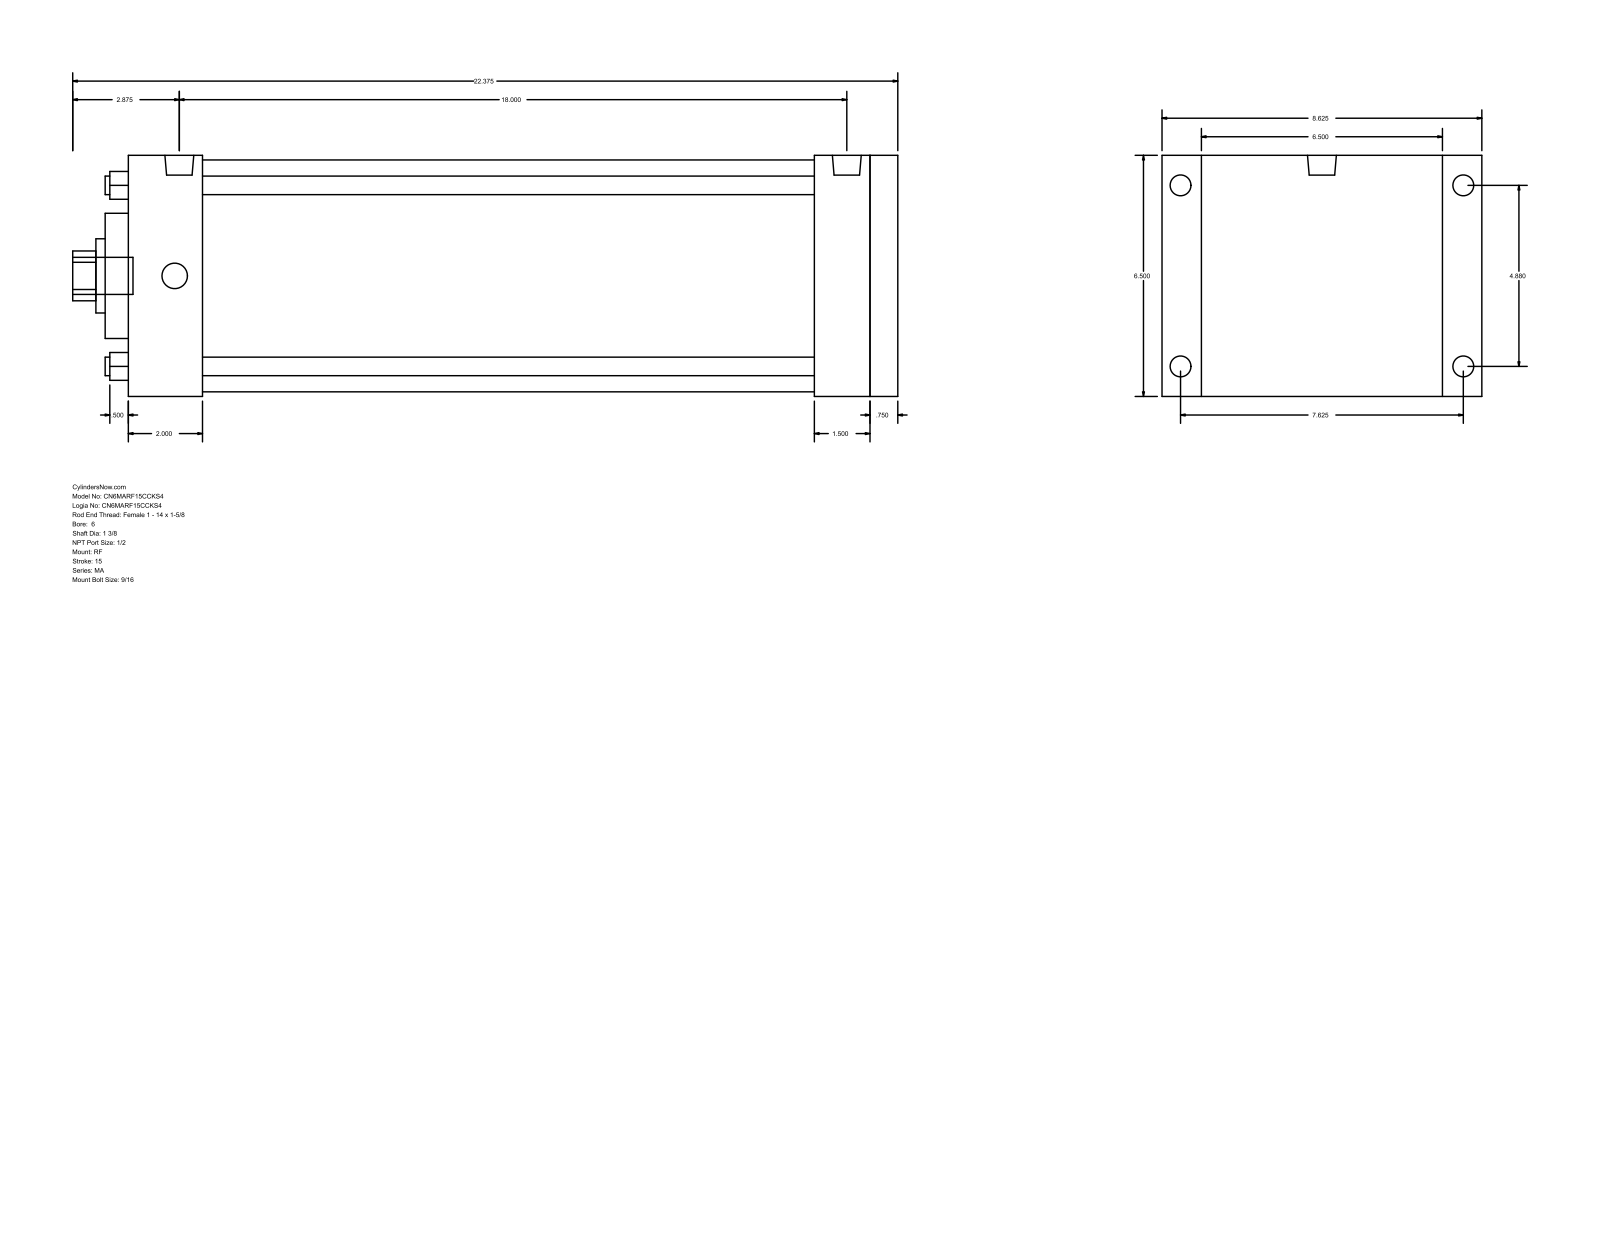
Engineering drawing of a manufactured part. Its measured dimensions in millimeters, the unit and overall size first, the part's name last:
Units: millimetres
Overall size (bounding box): 568.33 × 219.07 × 165.1
Round holes (diameter × count): ⌀12.7 ×4, ⌀34.92 ×1, ⌀50.8 ×1, ⌀85.72 ×1, ⌀158.75 ×1
Round bosses / shafts (diameter × count): ⌀17.46 ×4, ⌀14.29 ×4, ⌀19.77 ×2, ⌀25.4 ×1
Partial cylindrical surfaces — rounded edges, fillets, slot ends (radius × count): R17.06 ×1
Main face-to-face distances: 165.1, 530.23, 511.17, 19.06, 50.8, 460.37, 479.43, 473.08, 422.28, 38.09
Hole centre spacings: 87.65, 123.96, 175.31
Bodies: 0 solids, 94 faces (65 planar, 29 cylindrical, 0 other)
Part name (STEP PRODUCT): MA_RF__0600_1.375
STEP written by: GSSL Pune (CONFIG_CONTROL_DESIGN)
